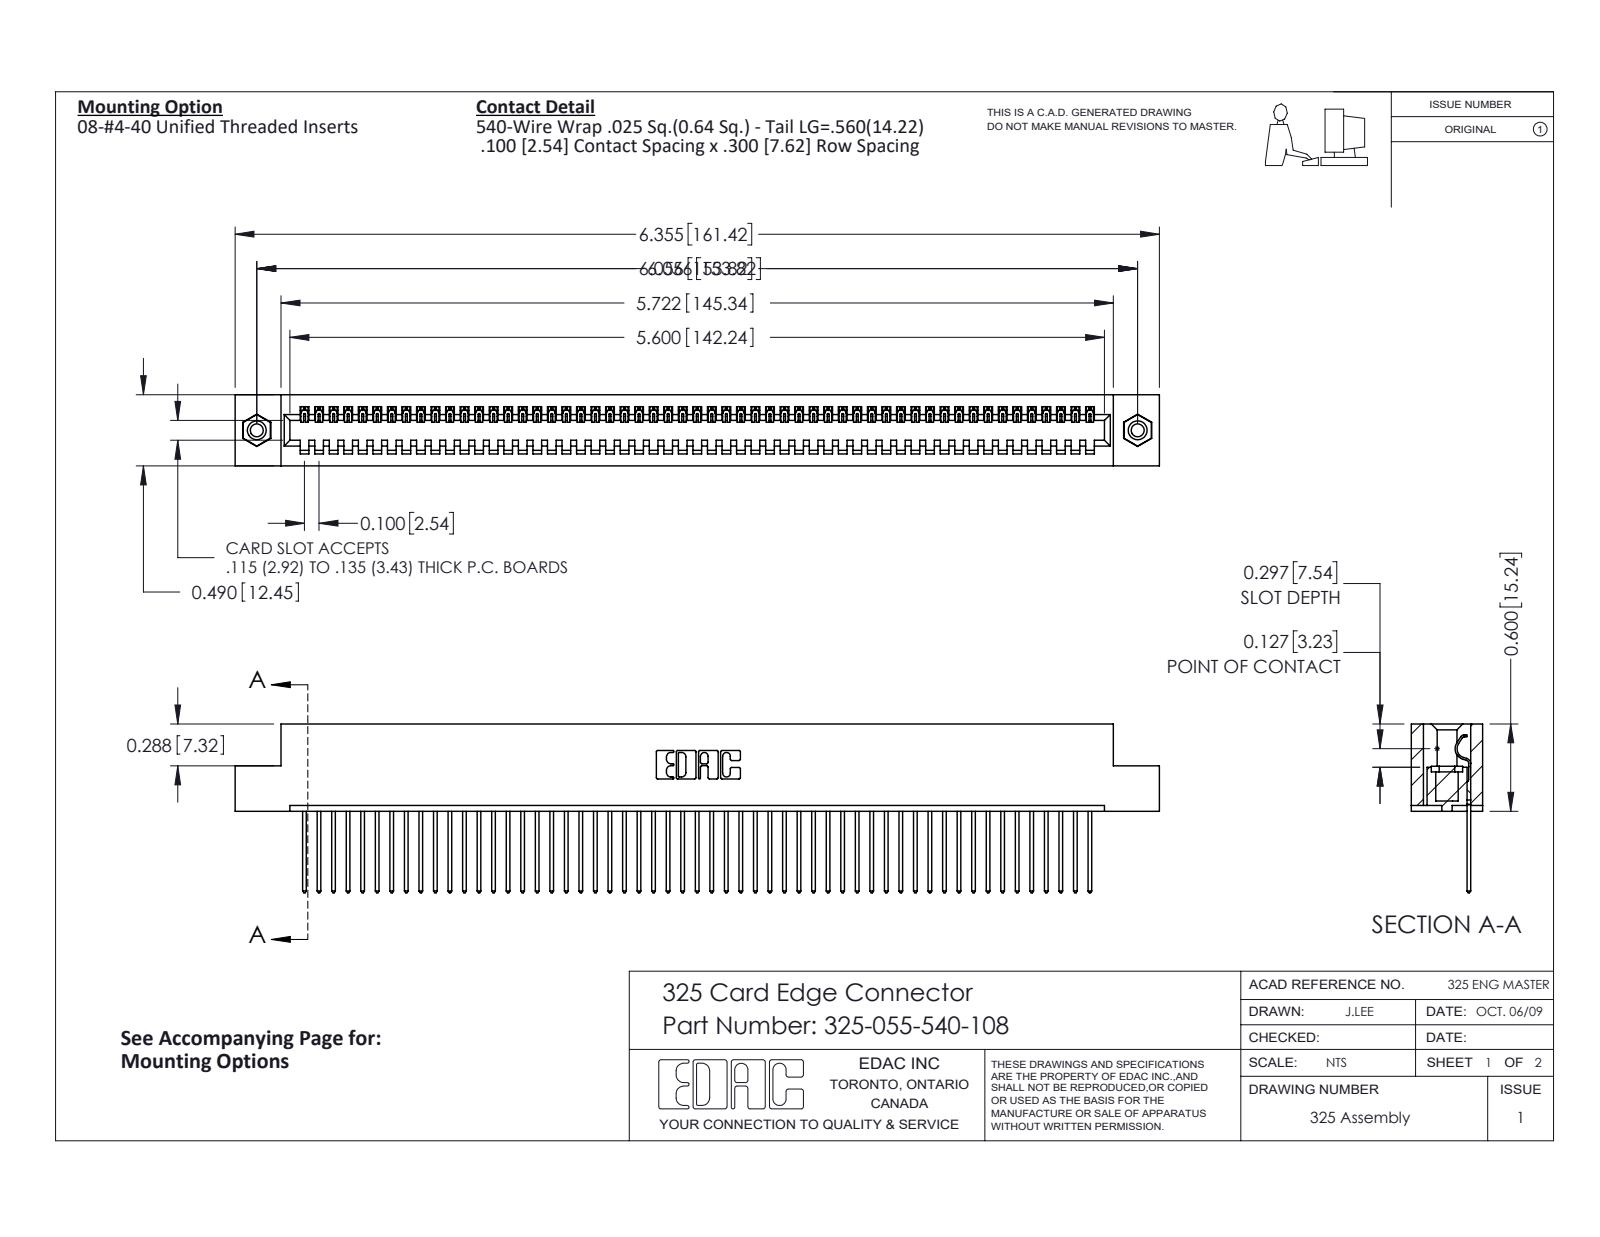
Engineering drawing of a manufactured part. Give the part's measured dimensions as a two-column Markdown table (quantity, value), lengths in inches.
| quantity | value |
| --- | --- |
| part name | 325-292-001_325-293-140; 345-250-001_345-250-003-102; 325-055-540-108; 325 Part_TI |
| STEP written by | SolidWorks 2016 (CONFIG_CONTROL_DESIGN) |
| units | inches |
| bodies | 58 solids, 3364 faces (2412 planar, 936 cylindrical, 16 other) |
| overall size | 6.355 × 1.16 × 0.49 |
| volume | 1.261 in³ |
| surface area | 36.21 in² |
| round holes (diameter × count) | 0.089 × 2, 0.125 × 2, 0.16 × 2 |
| round bosses / shafts (diameter × count) | 0.155 × 2 |
| partial cylindrical surfaces (radius × count) | 0.006 × 110, 0.01 × 110, 0.01 × 22, 0.007 × 6, 0.031 × 6, 0.026 × 3, 0.014 × 1, 0.022 × 1 |
| main face-to-face distances | 0.083, 0.407, 0.49, 0.107, 0.383, 0.025, 0.3, 0.325, 0.56, 0.263 |
| hole center spacings | 6.056 |
